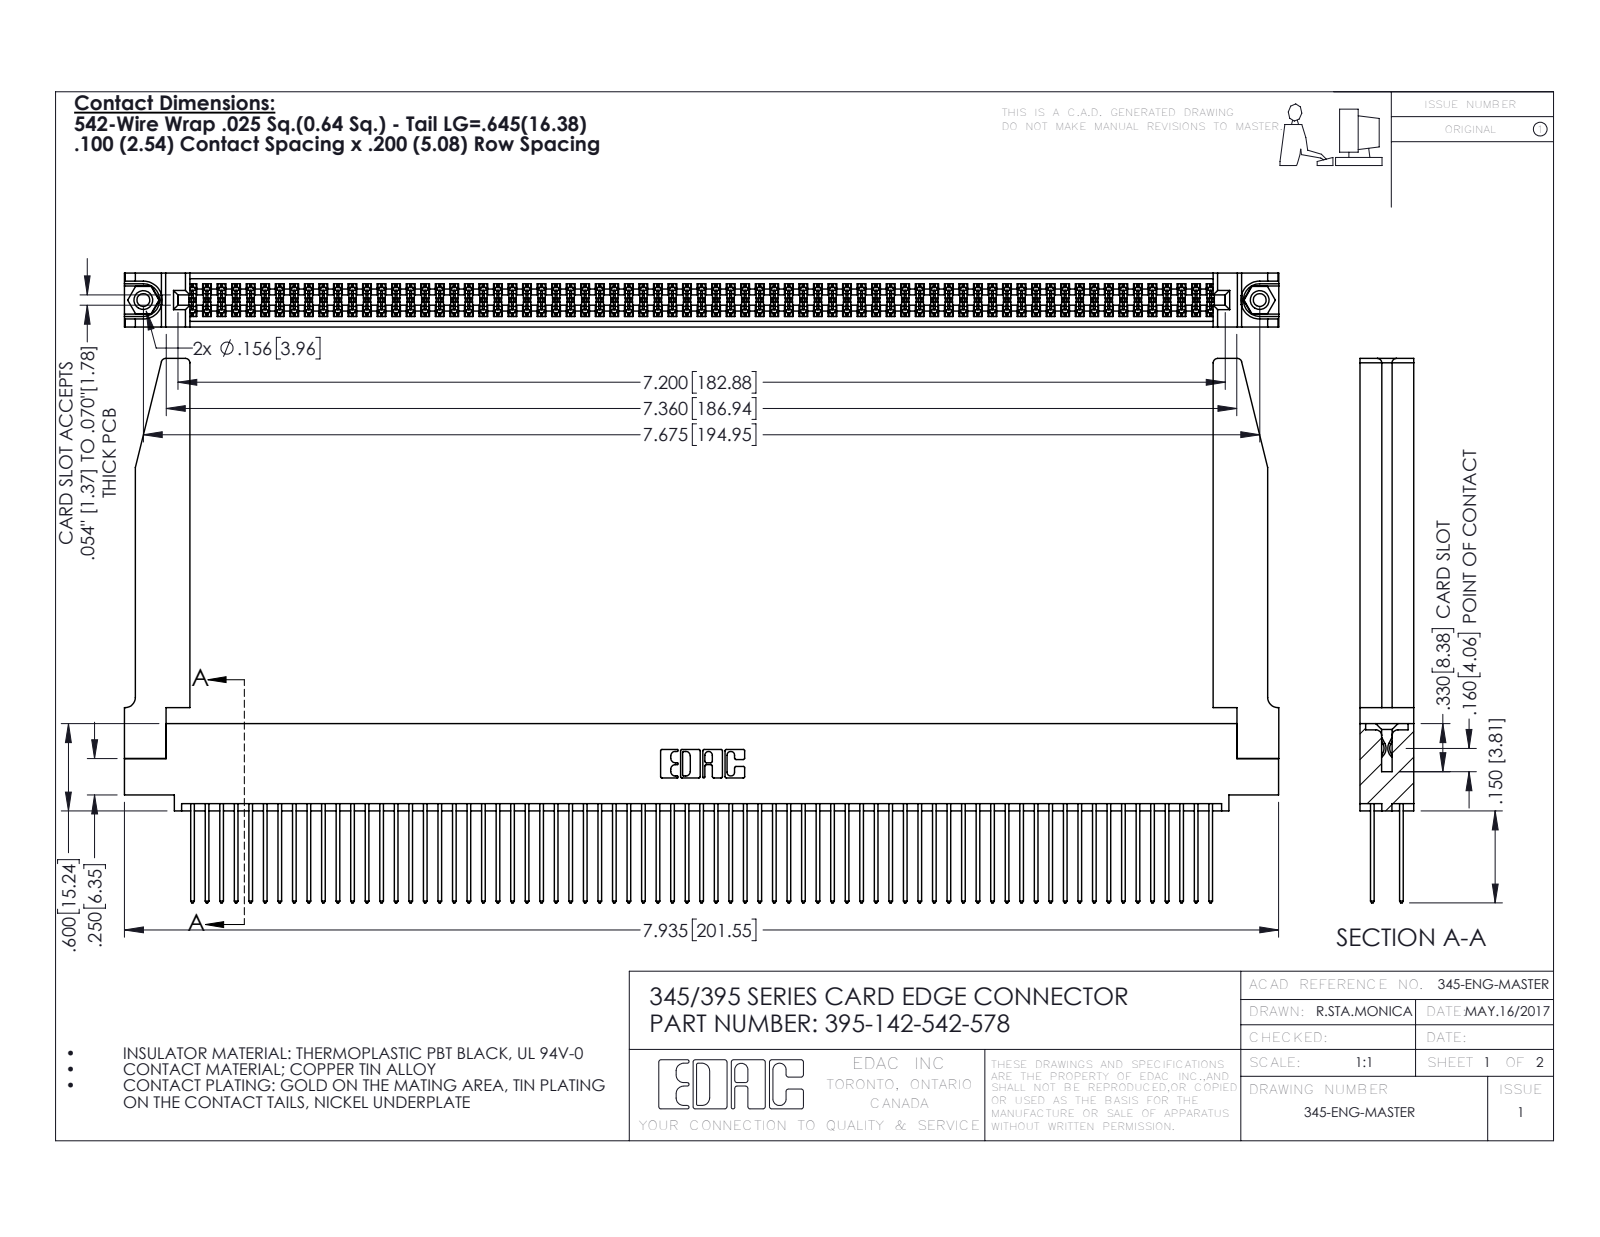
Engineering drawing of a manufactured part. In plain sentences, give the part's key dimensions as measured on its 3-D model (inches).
The part is named "345-292-001_345-293-142; 345-220-078_345-220-078; 395-142-542-578; 345-250-001_345-250-001-102 (+1 more)". Its 3-D file was written by "SolidWorks 2016 (CONFIG_CONTROL_DESIGN)". It is 147 solids with 7464 faces: 4912 planar, 2500 cylindrical and 52 other. Overall it measures 7.936 by 3.742 by 0.37 inches. Its volume is 1.721 cubic inches and its surface area 63.24 square inches. Round holes: 2 of diameter 0.089, 2 of diameter 0.125, 2 of diameter 0.156, 1 of diameter 0.064. Round bosses or shafts: 2 of diameter 0.155. Partial cylindrical surfaces (rounded edges, fillets, slot ends): 213 of radius 0.006, 142 of radius 0.01, 22 of radius 0.01, 8 of radius 0.03, 6 of radius 0.007, 6 of radius 0.031, 3 of radius 0.026, 2 of radius 0.014. The main face-to-face distances are 0.072, 0.298, 0.37, 0.098, 0.272, 0.025, 0.2, 0.225, 0.175, 0.149. The hole center spacings are 0.27, 7.439, 7.675.
